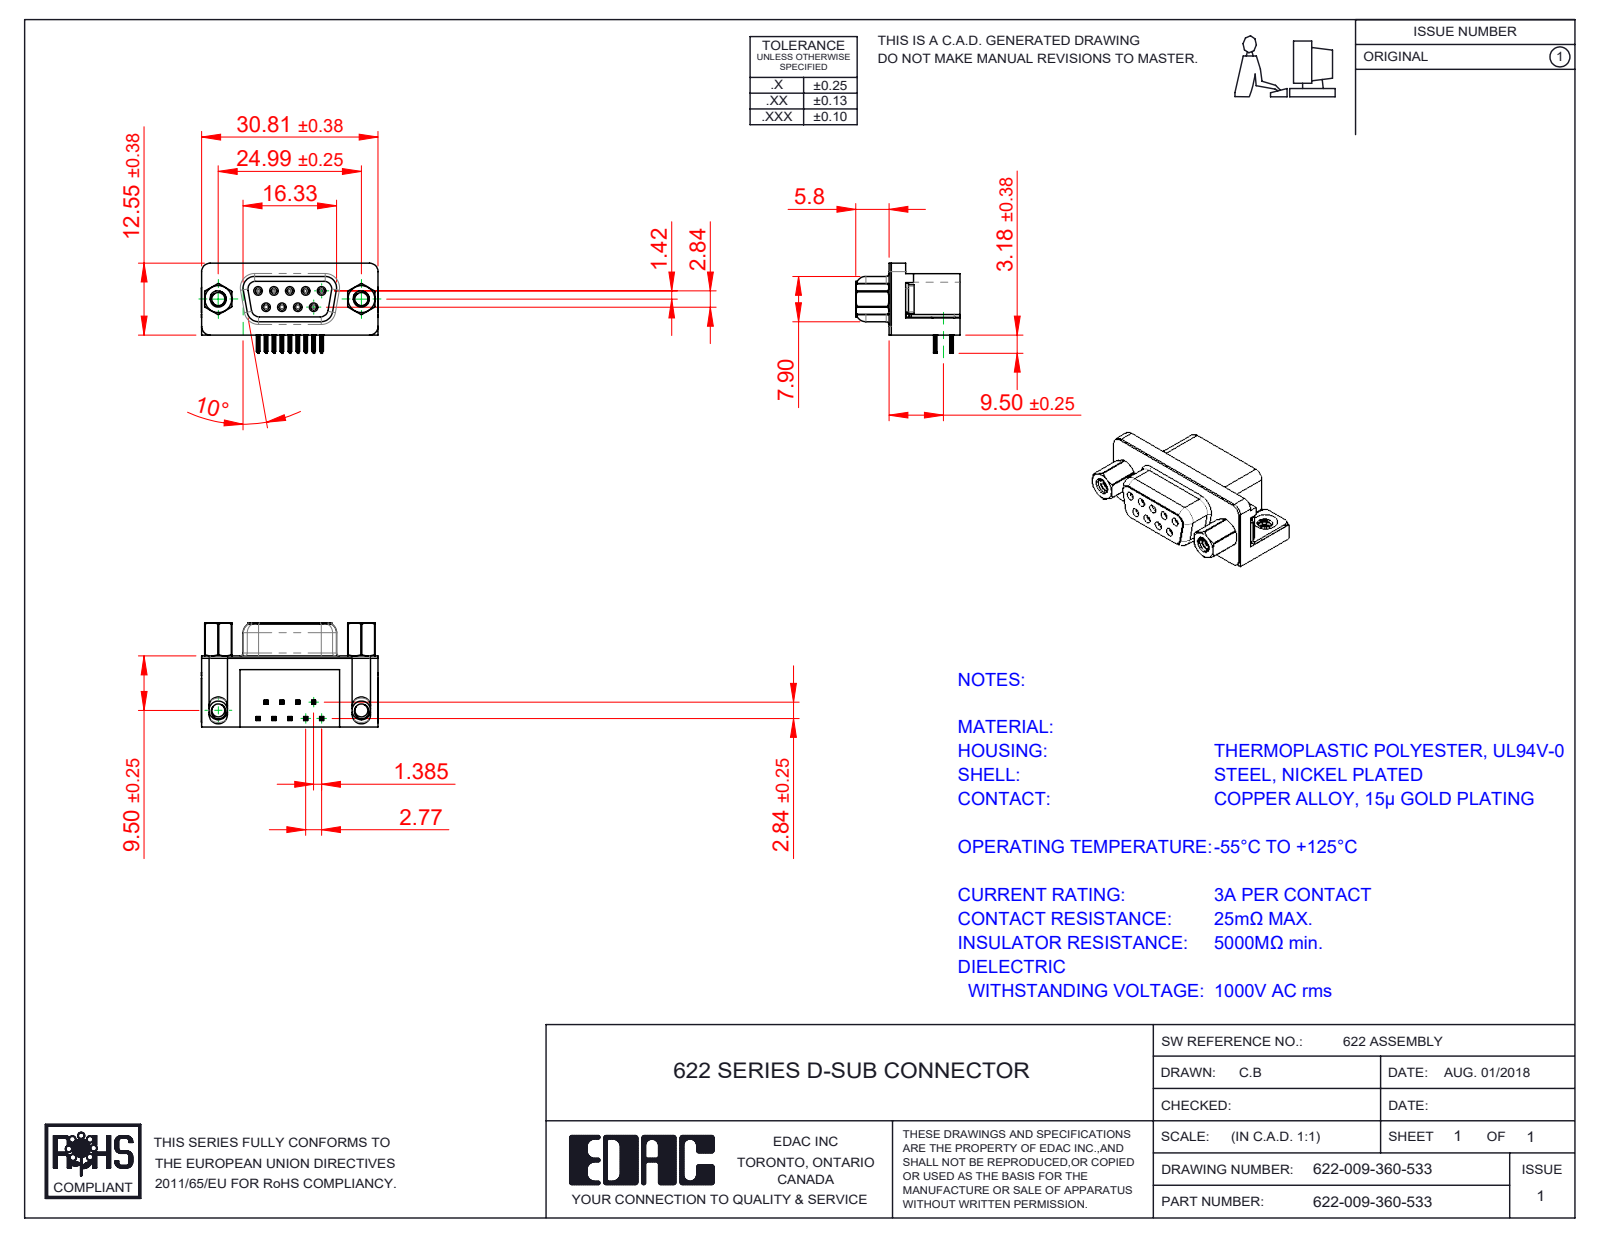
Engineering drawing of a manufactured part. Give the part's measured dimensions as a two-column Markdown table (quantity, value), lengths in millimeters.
| quantity | value |
| --- | --- |
| part name | 622 Shell_9 Socket; 622 4-40 Hex Standoff 5; 622-009-360-533; 622 Socket Bottom (+4 more) |
| STEP written by | SolidWorks 2016 (CONFIG_CONTROL_DESIGN) |
| units | millimeters |
| bodies | 17 solids, 1732 faces (738 planar, 488 cylindrical, 506 other) |
| overall size | 30.89 × 18.2 × 16.25 |
| volume | 3 927 mm³ |
| surface area | 5 532 mm² |
| round holes (diameter × count) | 0.8 × 9, 0.9 × 9, 2.26 × 2, 2.29 × 2, 4 × 2, 4.8 × 2, 5 × 2 |
| round bosses / shafts (diameter × count) | 1.2 × 9, 4.9 × 2, 4.75 × 2, 3.9 × 2, 2.79 × 2 |
| partial cylindrical surfaces (radius × count) | 0.1 × 72, 0.15 × 36, 0.35 × 18, 1 × 18, 0.5 × 10, 0.34 × 9, 0.25 × 8, 1.35 × 8 |
| main face-to-face distances | 0.4, 12, 12.4, 6.2, 0.35, 2.9, 2.5, 10.34, 0.5, 5.8 |
| hole center spacings | 3.16, 2.77, 5.54, 5.03, 5.04, 8.31, 7.48, 7.49 |
